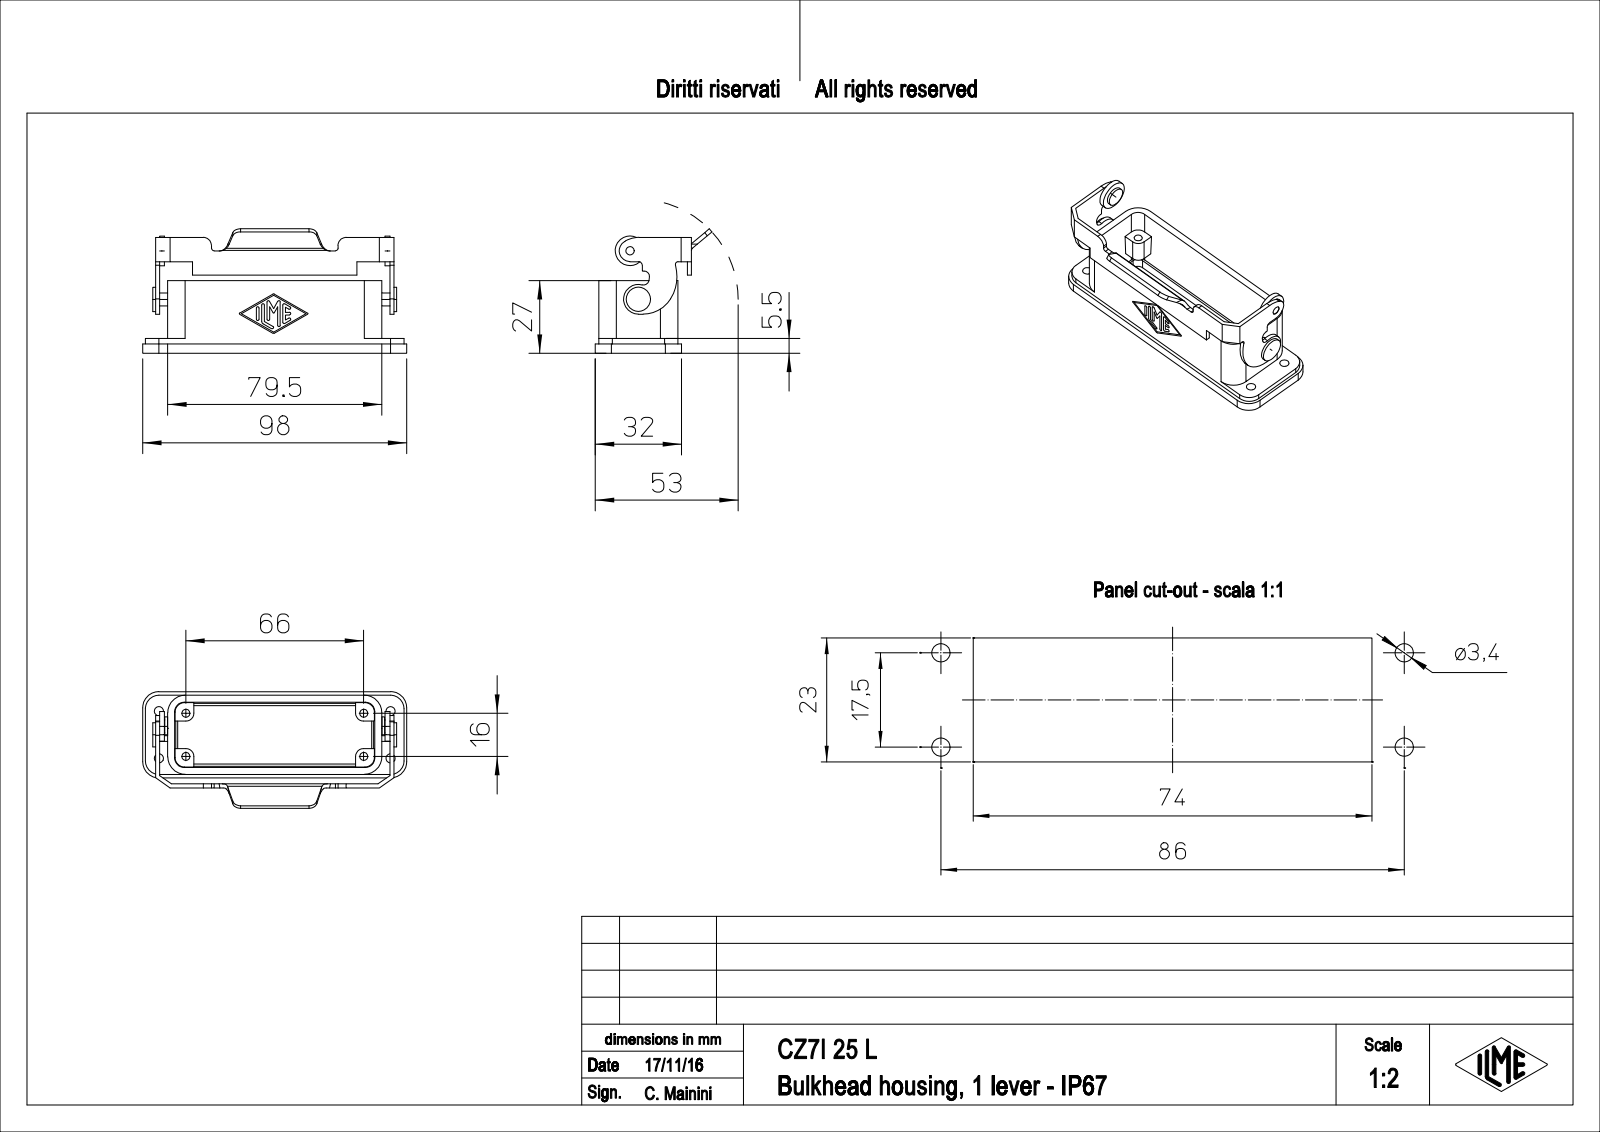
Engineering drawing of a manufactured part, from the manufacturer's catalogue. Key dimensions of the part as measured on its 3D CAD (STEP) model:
Part name (STEP PRODUCT): CZ7I_25_L
STEP written by: PTC Creo Elements/Direct Modeling 19.0E 27-Jun-2016 (C) Parametric Technology GmbH (AUTOMOTIVE_DESIGN)
Units: millimetres
Bodies: 1 solid, 210 faces (100 planar, 110 cylindrical, 0 other)
Overall size (bounding box): 98 × 46.2 × 43.28
Volume: 24 369 mm³ · Surface area: 20 198 mm²
Round holes (diameter × count): ⌀3 ×4, ⌀3.4 ×4, ⌀3.1 ×1, ⌀5 ×1
Round bosses / shafts (diameter × count): ⌀4.8 ×2, ⌀11 ×1, ⌀9 ×1, ⌀7 ×1, ⌀3 ×1
Partial cylindrical surfaces — rounded edges, fillets, slot ends (radius × count): R3 ×10, R3.5 ×7, R2.5 ×5, R1 ×4, R5 ×4, R6 ×4, R6.5 ×4, R2 ×2
Main face-to-face distances: 1.5, 29.4, 3.5, 5, 87, 34.4, 32.9, 84, 5.5, 4.5
Hole centre spacings: 10.03, 19.51, 76, 77.82, 16, 17.5, 66, 67.91
